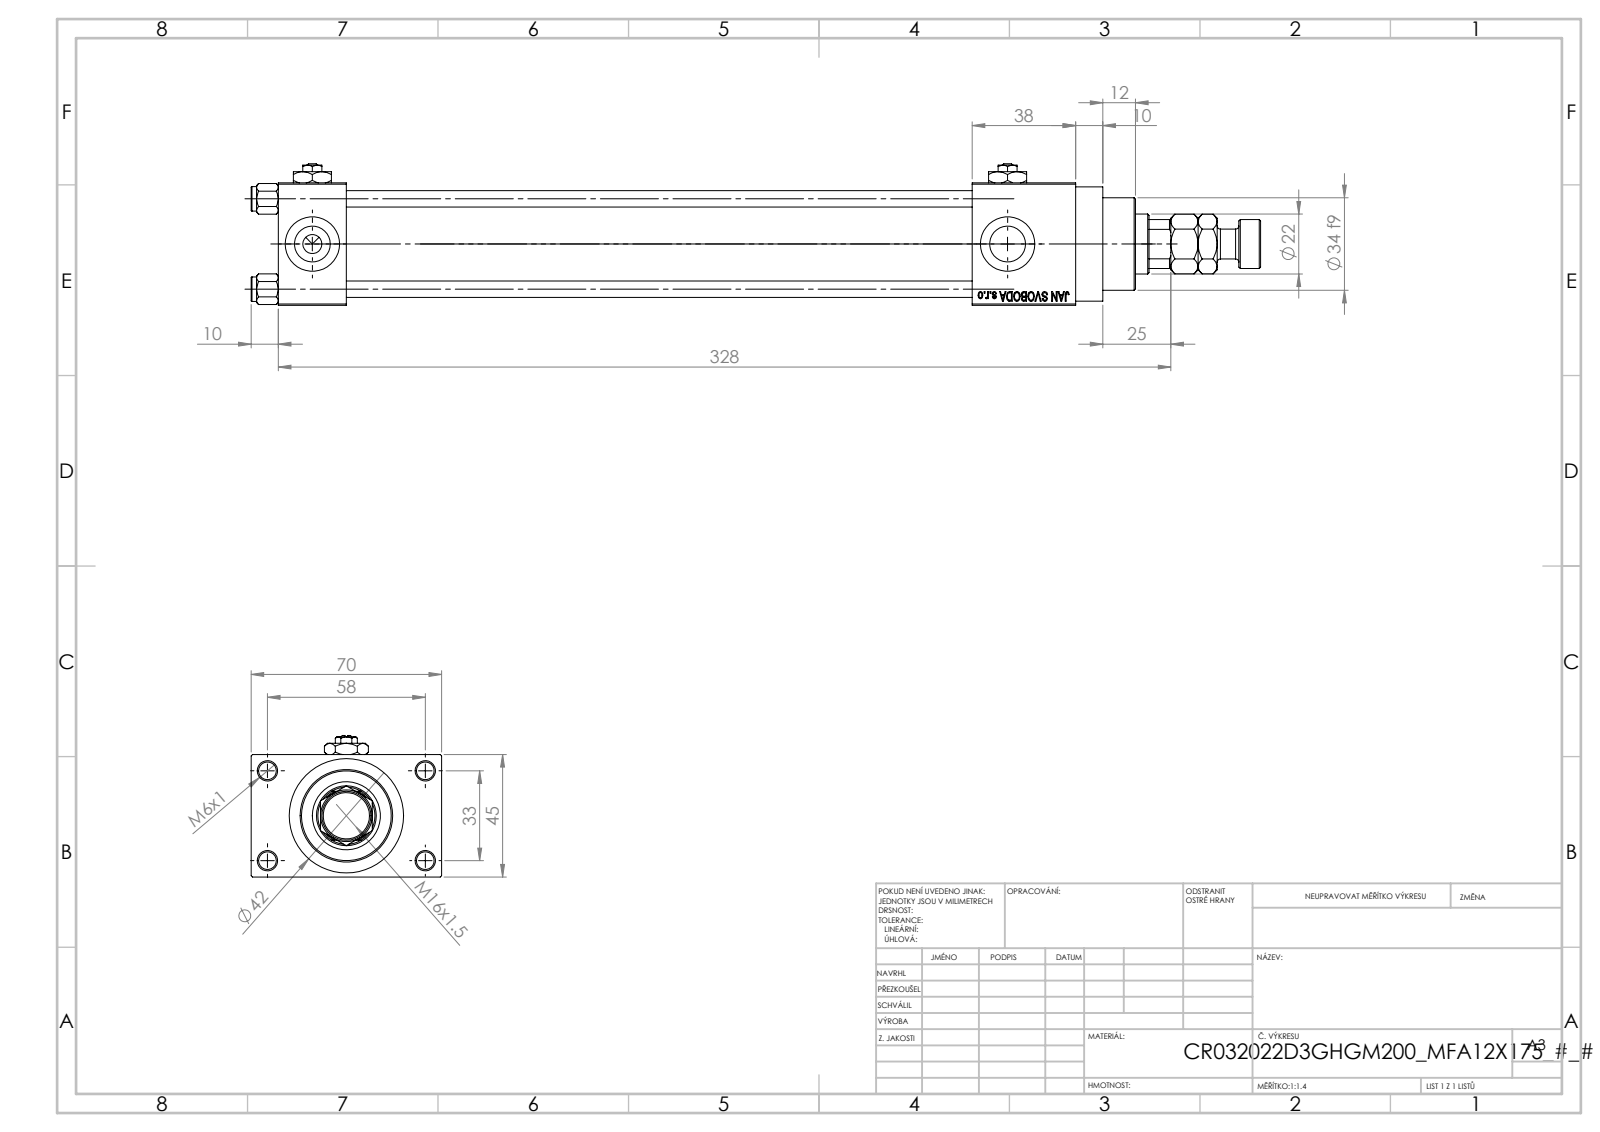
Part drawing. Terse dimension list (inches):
name: V215CR_VCP_D; NUT_M5_D; V215_VC_A; Zatka_pro_OIL_PORT (+3 more)
written by: SolidWorks 2019 (CONFIG_CONTROL_DESIGN)
unit: in
bodies: 14 solids, 1253 faces (558 planar, 103 cylindrical, 592 other)
size: 14.606 × 2.756 × 2.047
volume: 24.29 in³; area: 232.5 in²
holes: 4× ⌀0.236, 4× ⌀0.256, 4× ⌀0.518, 4× ⌀0.787, 3× ⌀0.276, 1× ⌀0.413, 1× ⌀0.866, 1× ⌀0.945, 1× ⌀0.984, 1× ⌀1.26, 1× ⌀1.299
bosses: 4× ⌀0.354, 1× ⌀1.654, 1× ⌀1.496, 1× ⌀1.339, 1× ⌀0.709, 1× ⌀0.433
rounds: 1× R0.413
face distances: 1.772, 0.984, 0.492, 9.055, 10.039, 2.264, 10.551, 1.496, 11.535, 2.756
hole spacings: 0.488, 0.924, 1.307, 1.314, 1.392, 1.795, 2.219, 1.299
